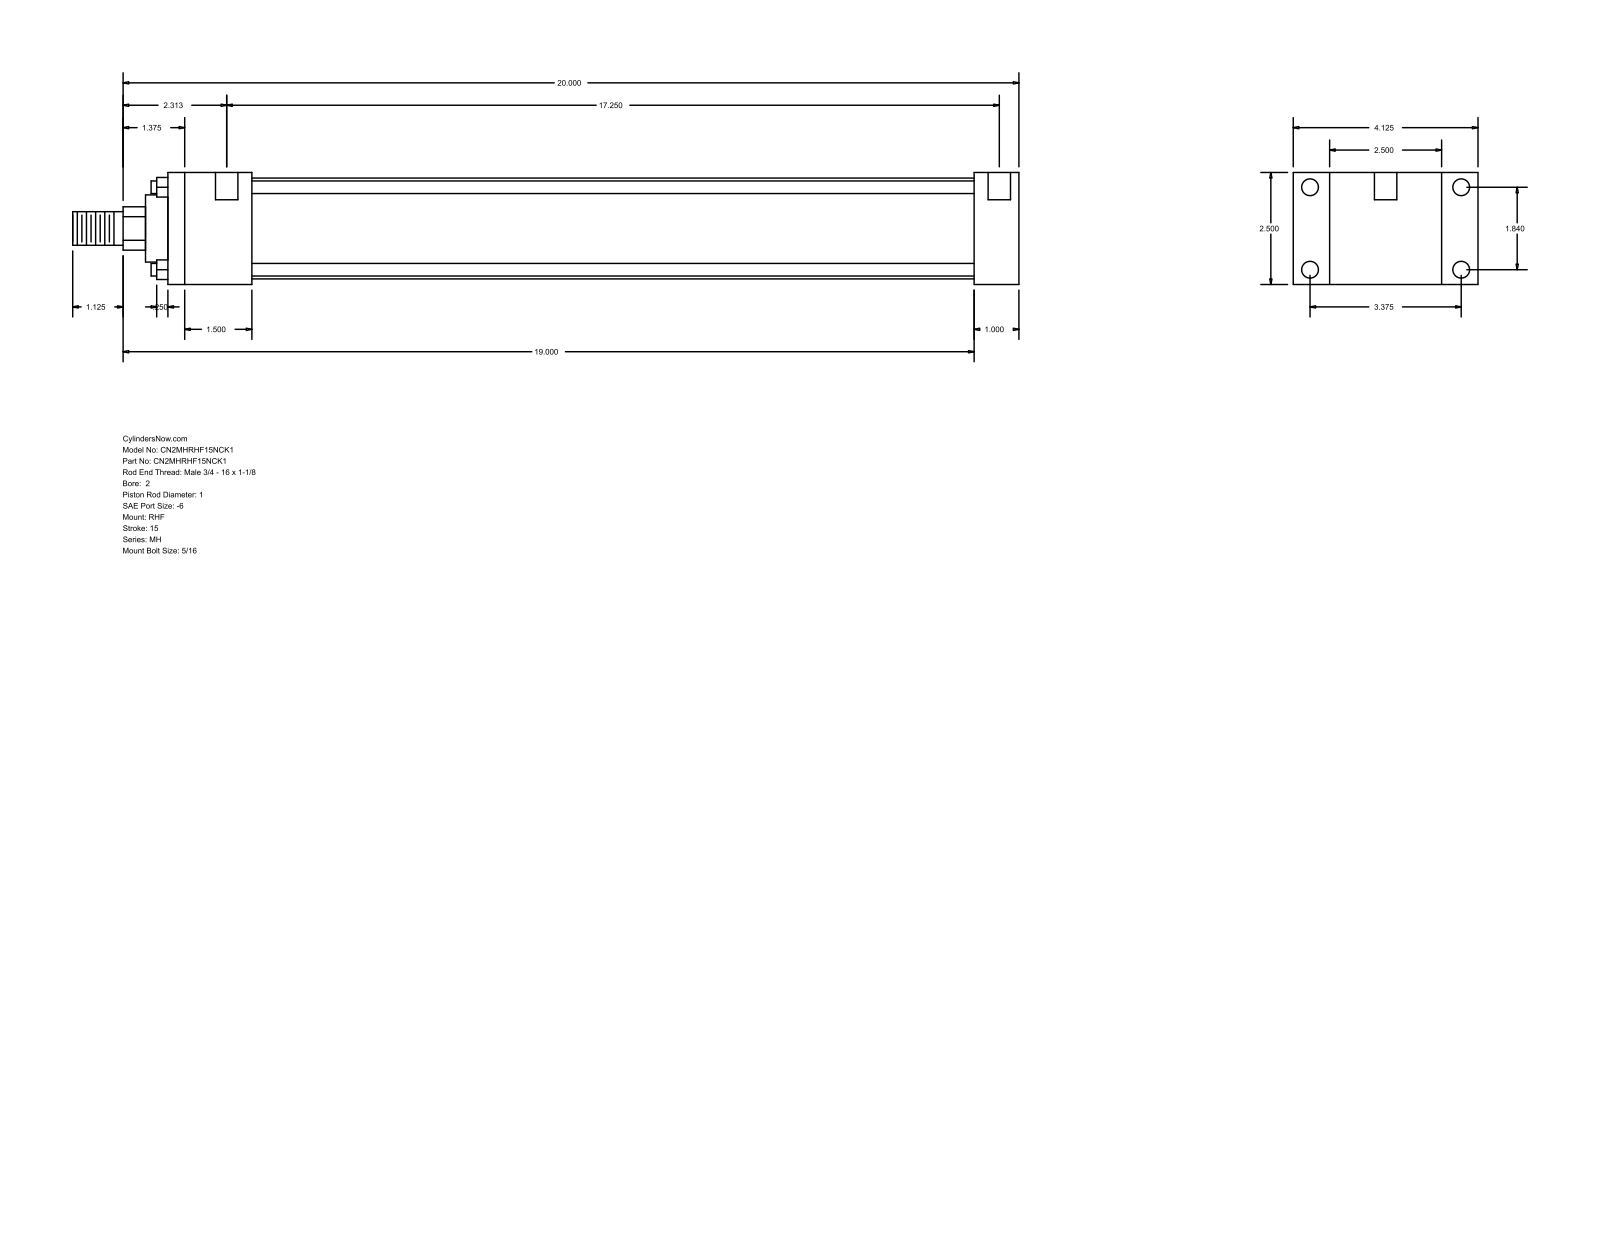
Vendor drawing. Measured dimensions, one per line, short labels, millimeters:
name: MH_RHF__0200_1
written by: GSSL Pune (CONFIG_CONTROL_DESIGN)
unit: mm
bodies: 0 solids, 88 faces (60 planar, 28 cylindrical, 0 other)
size: 536.58 × 104.78 × 63.5
holes: 4× ⌀5.56, 4× ⌀9.53, 2× ⌀12.7
bosses: 4× ⌀7.14, 1× ⌀57.15, 1× ⌀38.1, 1× ⌀25.4, 1× ⌀19.05
rounds: 1× R12.29
face distances: 63.5, 25.4, 20.64, 84.14, 482.6, 457.2, 104.78, 47.63, 409.57, 434.97
hole spacings: 46.74, 85.72, 97.63, 446.08, 3.17, 4.76, 438.15, 441.32
